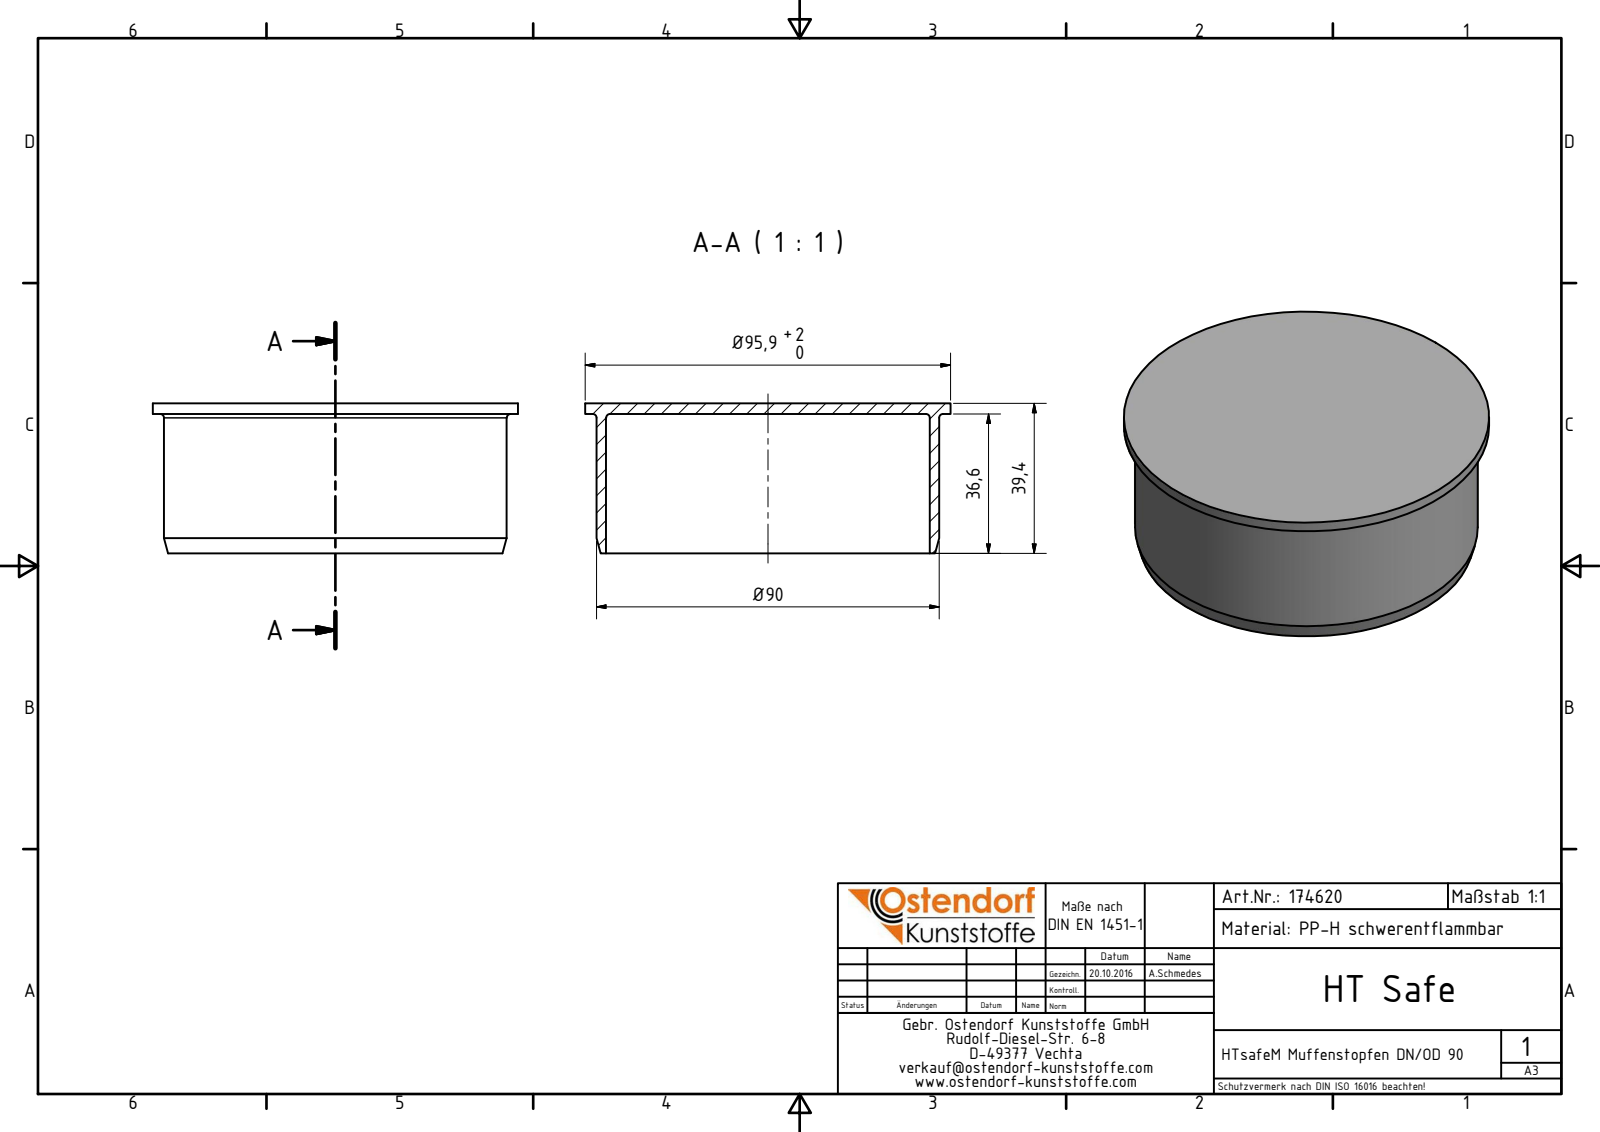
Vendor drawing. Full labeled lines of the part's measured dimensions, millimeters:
Part name (STEP PRODUCT): 174620 HTsafeM DN_OD 90
STEP written by: Autodesk Inventor 2016 (AUTOMOTIVE_DESIGN)
Units: millimetres
Bodies: 1 solid, 10 faces (4 planar, 3 cylindrical, 3 other)
Overall size (bounding box): 95.9 × 95.9 × 39.4
Volume: 44 894 mm³ · Surface area: 34 902 mm²
Round holes (diameter × count): ⌀85 ×1
Round bosses / shafts (diameter × count): ⌀95.9 ×1, ⌀90 ×1
Main face-to-face distances: 2.8, 36.6, 39.4
